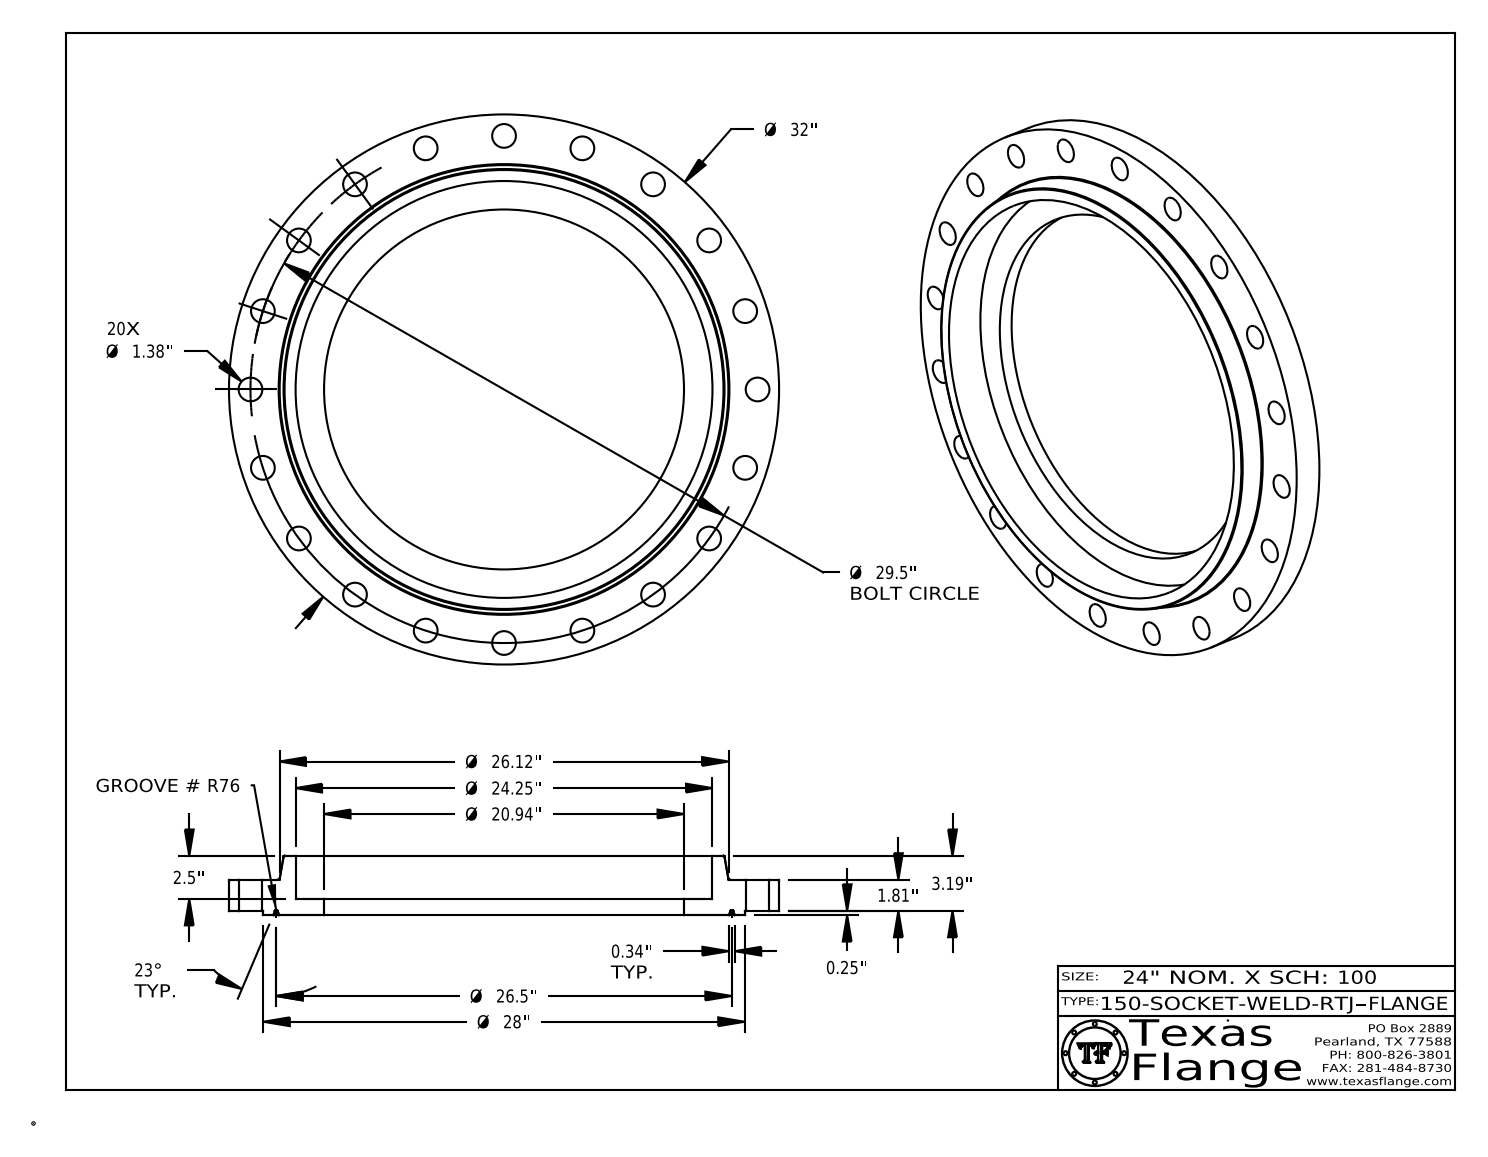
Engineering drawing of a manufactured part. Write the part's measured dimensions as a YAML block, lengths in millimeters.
part_name: "150-SOCKET-WELD-RTJ"
step_written_by: "CATIA V5 STEP AP214 (AUTOMOTIVE_DESIGN)"
units: millimeters
bodies: {solids: 1, faces: 454, planar: 372, cylindrical: 68, other: 14}
overall_size: [812.8, 812.8, 87.4]
volume: 13080000
surface_area: 1026000
round_holes:
  - {diameter: 35.1, count: 20}
  - {diameter: 12.6, count: 1}
  - {diameter: 531.8, count: 1}
  - {diameter: 616, count: 1}
round_bosses_or_shafts:
  - {diameter: 0.8, count: 8}
  - {diameter: 812.8, count: 1}
  - {diameter: 711.2, count: 1}
  - {diameter: 9.9, count: 1}
face_to_face_distances: [52.3, 6.4, 46, 23.9, 17.5, 28.4, 87.4, 81, 63.5, 35.1]
hole_center_spacings: [374.7, 740.1, 117.2, 440.4, 529.8, 606.2, 667.6, 231.5]
